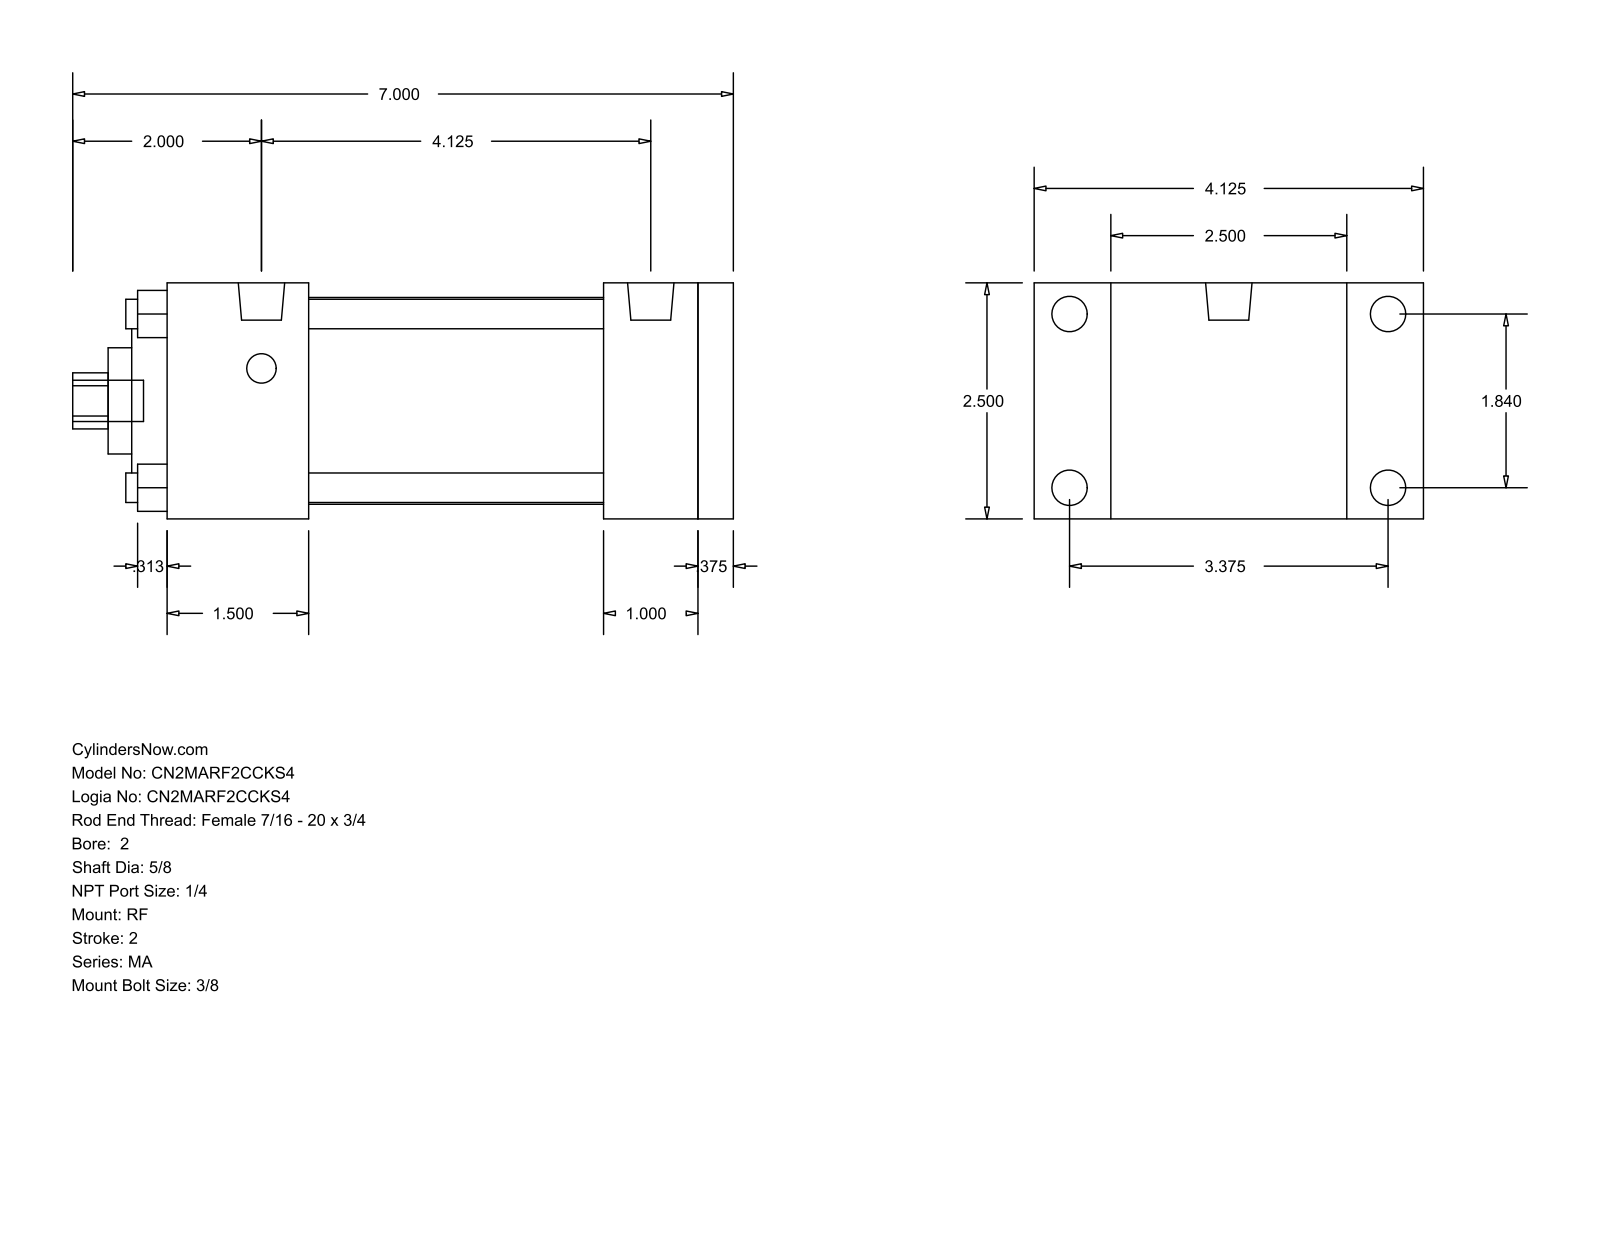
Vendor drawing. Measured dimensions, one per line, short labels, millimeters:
name: MA_RF__0200_0.625
written by: GSSL Pune (CONFIG_CONTROL_DESIGN)
unit: mm
bodies: 0 solids, 94 faces (65 planar, 29 cylindrical, 0 other)
size: 177.8 × 104.78 × 63.5
holes: 4× ⌀7.94, 1× ⌀15.88, 1× ⌀28.57, 1× ⌀50.8, 1× ⌀55.63
bosses: 4× ⌀9.53, 4× ⌀7.94, 2× ⌀12.49, 1× ⌀11.11
rounds: 1× R7.54
face distances: 63.5, 9.52, 152.4, 104.78, 25.4, 38.1, 142.88, 114.3, 117.48, 79.38
hole spacings: 33.05, 46.74, 66.1
